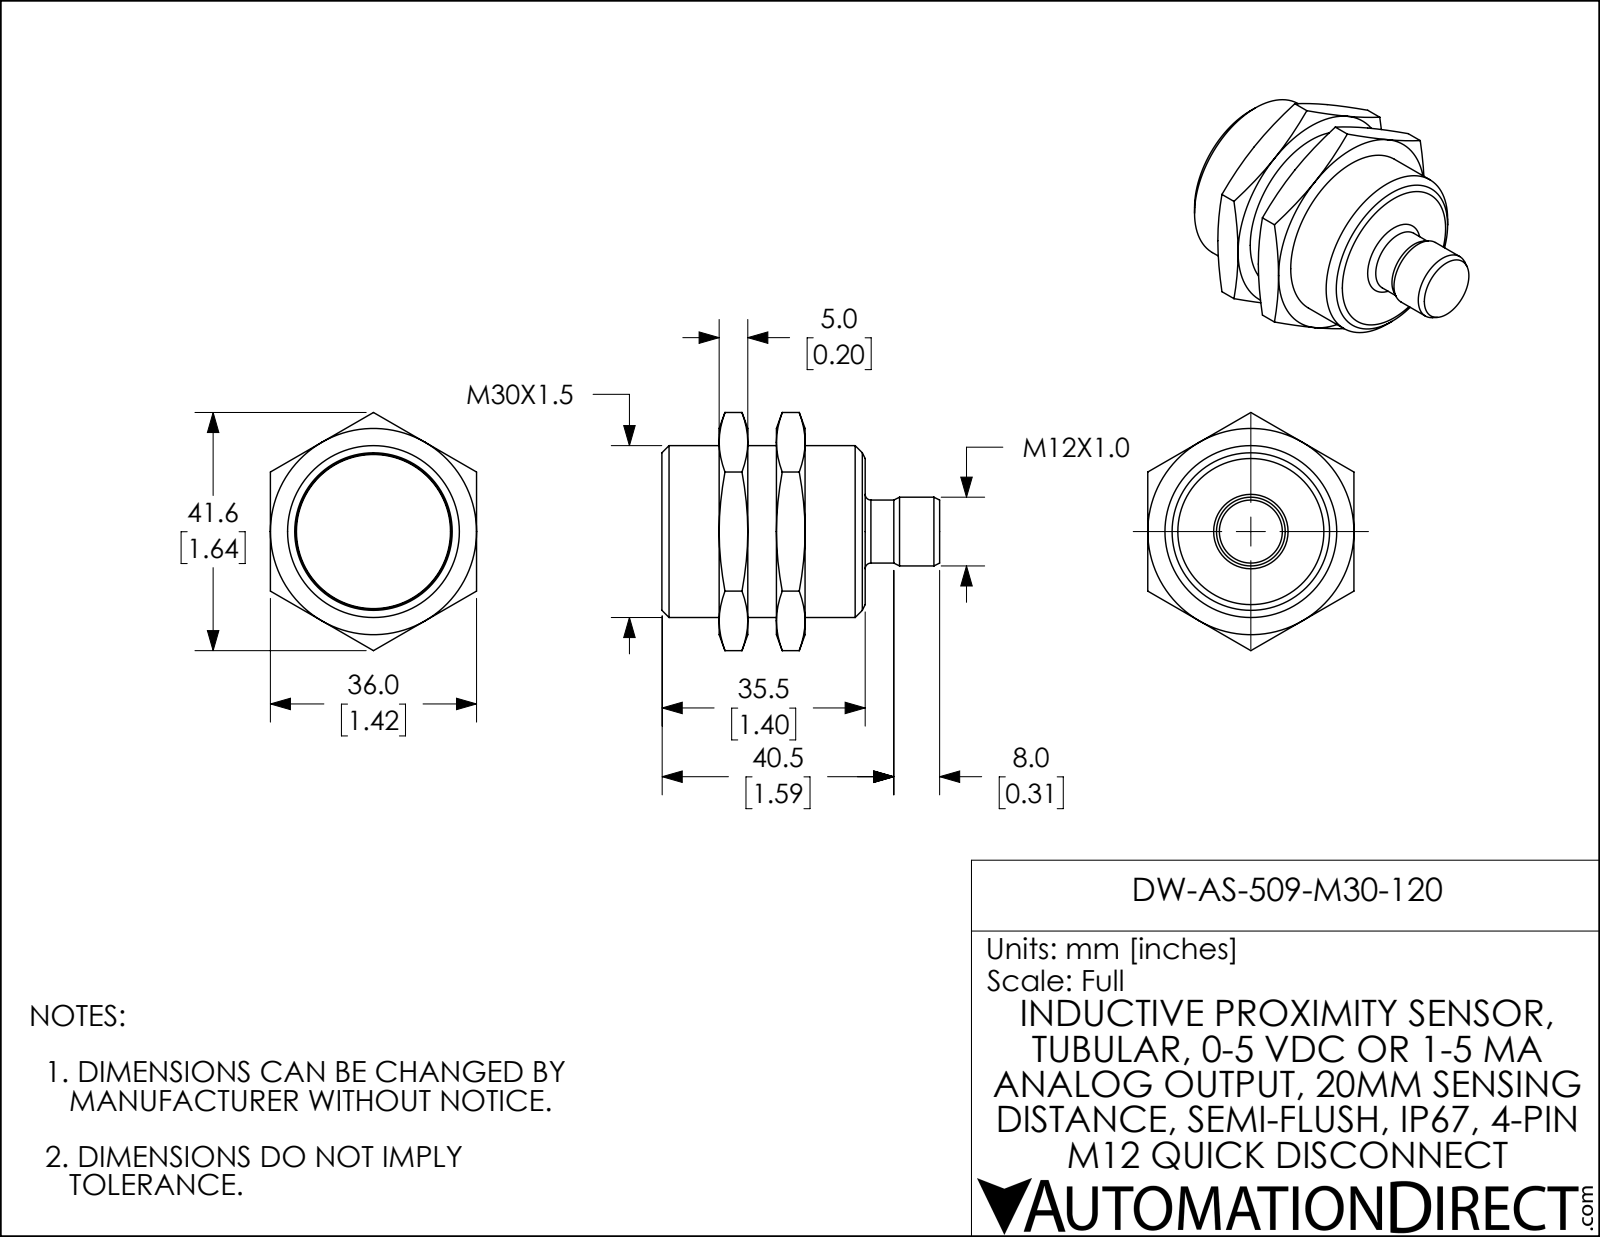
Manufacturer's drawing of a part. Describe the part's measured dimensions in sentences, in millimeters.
The part is named "DW-AS-50x-M30-120". Its 3-D file was written by "SolidWorks 2018 (AUTOMOTIVE_DESIGN)". It is 1 solid with 19 faces: 3 planar, 7 cylindrical and 9 other. Overall it measures 48.5 by 30 by 30 millimeters. Its volume is 26 240 cubic millimeters and its surface area 5 069 square millimeters. Round holes: 2 of diameter 1. Round bosses or shafts: 1 of diameter 30, 1 of diameter 12, 1 of diameter 11. The main face-to-face distances are 35.5, 13, 48.5.
